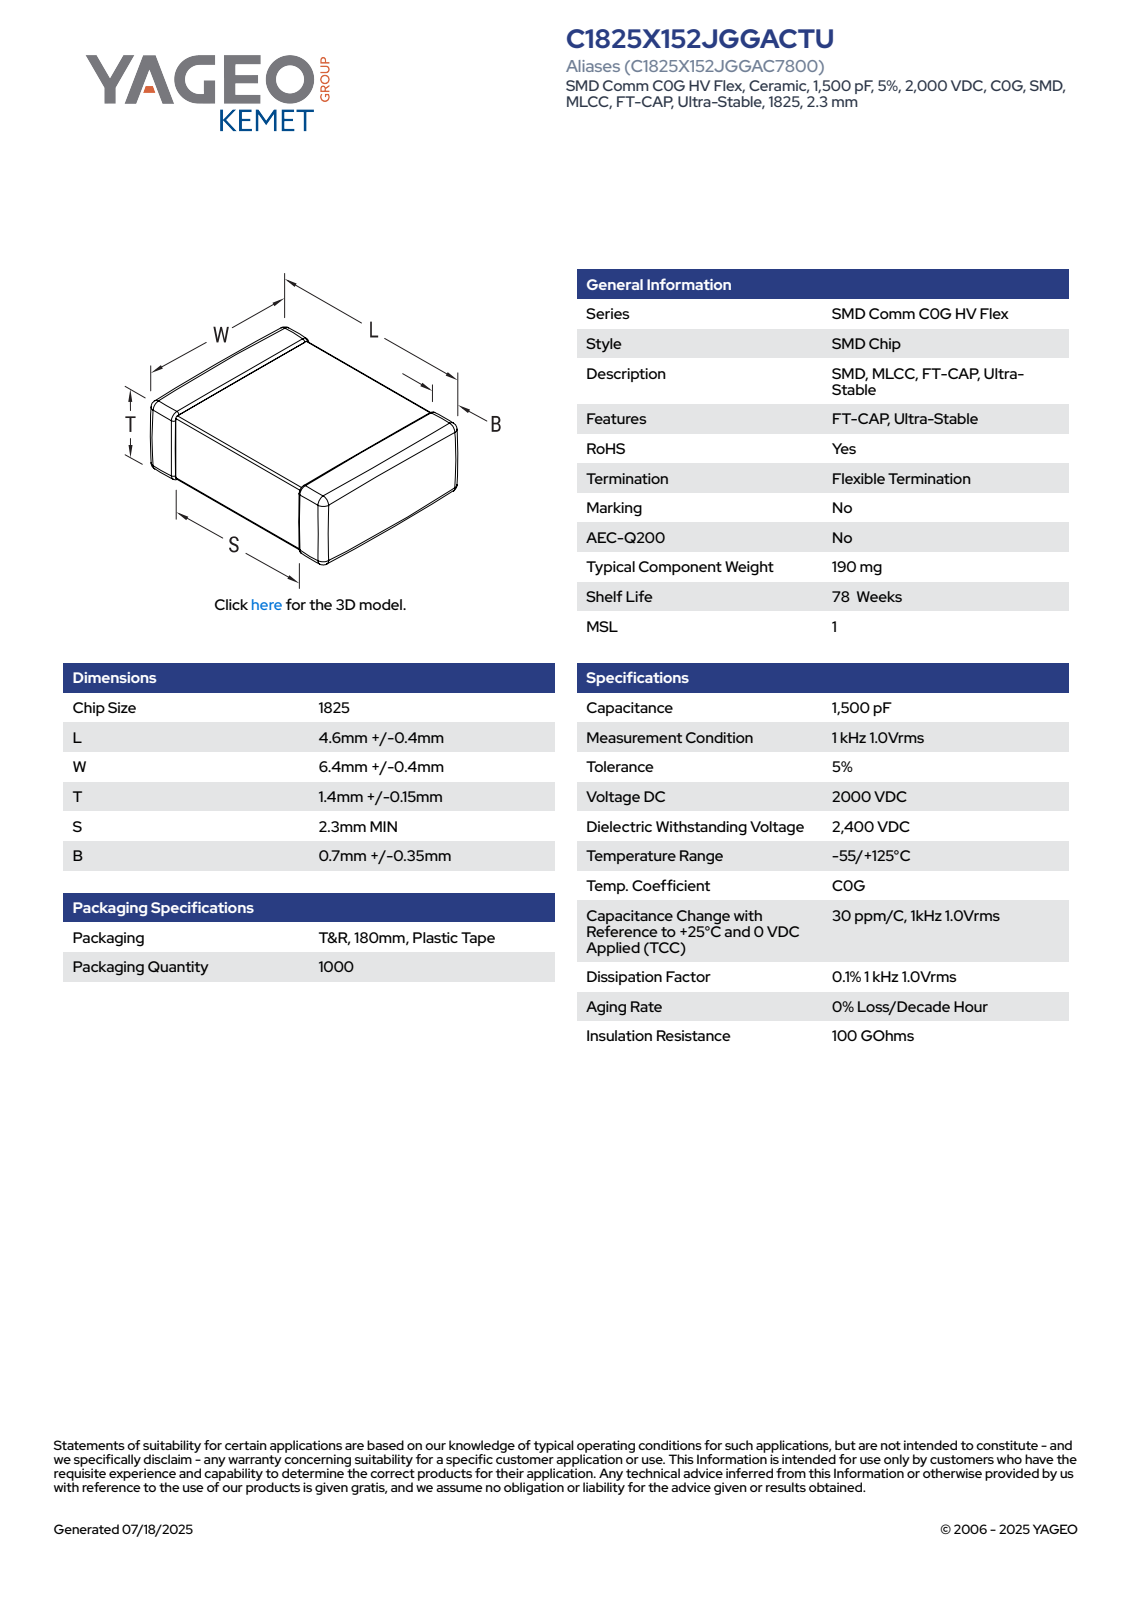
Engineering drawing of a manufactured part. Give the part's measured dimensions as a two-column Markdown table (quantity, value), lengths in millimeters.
| quantity | value |
| --- | --- |
| part name | CCS_CCSTDNOS_1825_L5W6.8T1.55B1.05 |
| STEP written by | SolidWorks 2014 (AUTOMOTIVE_DESIGN) |
| units | millimeters |
| bodies | 4 solids, 121 faces (71 planar, 34 cylindrical, 16 other) |
| overall size | 6.8 × 5 × 1.55 |
| volume | 46 mm³ |
| surface area | 101 mm² |
| partial cylindrical surfaces (radius × count) | 0.14 × 24 |
| main face-to-face distances | 1.41, 1.27, 1.55, 5, 6.66, 6.52, 6.8, 3.54, 3.12, 0.36 |
